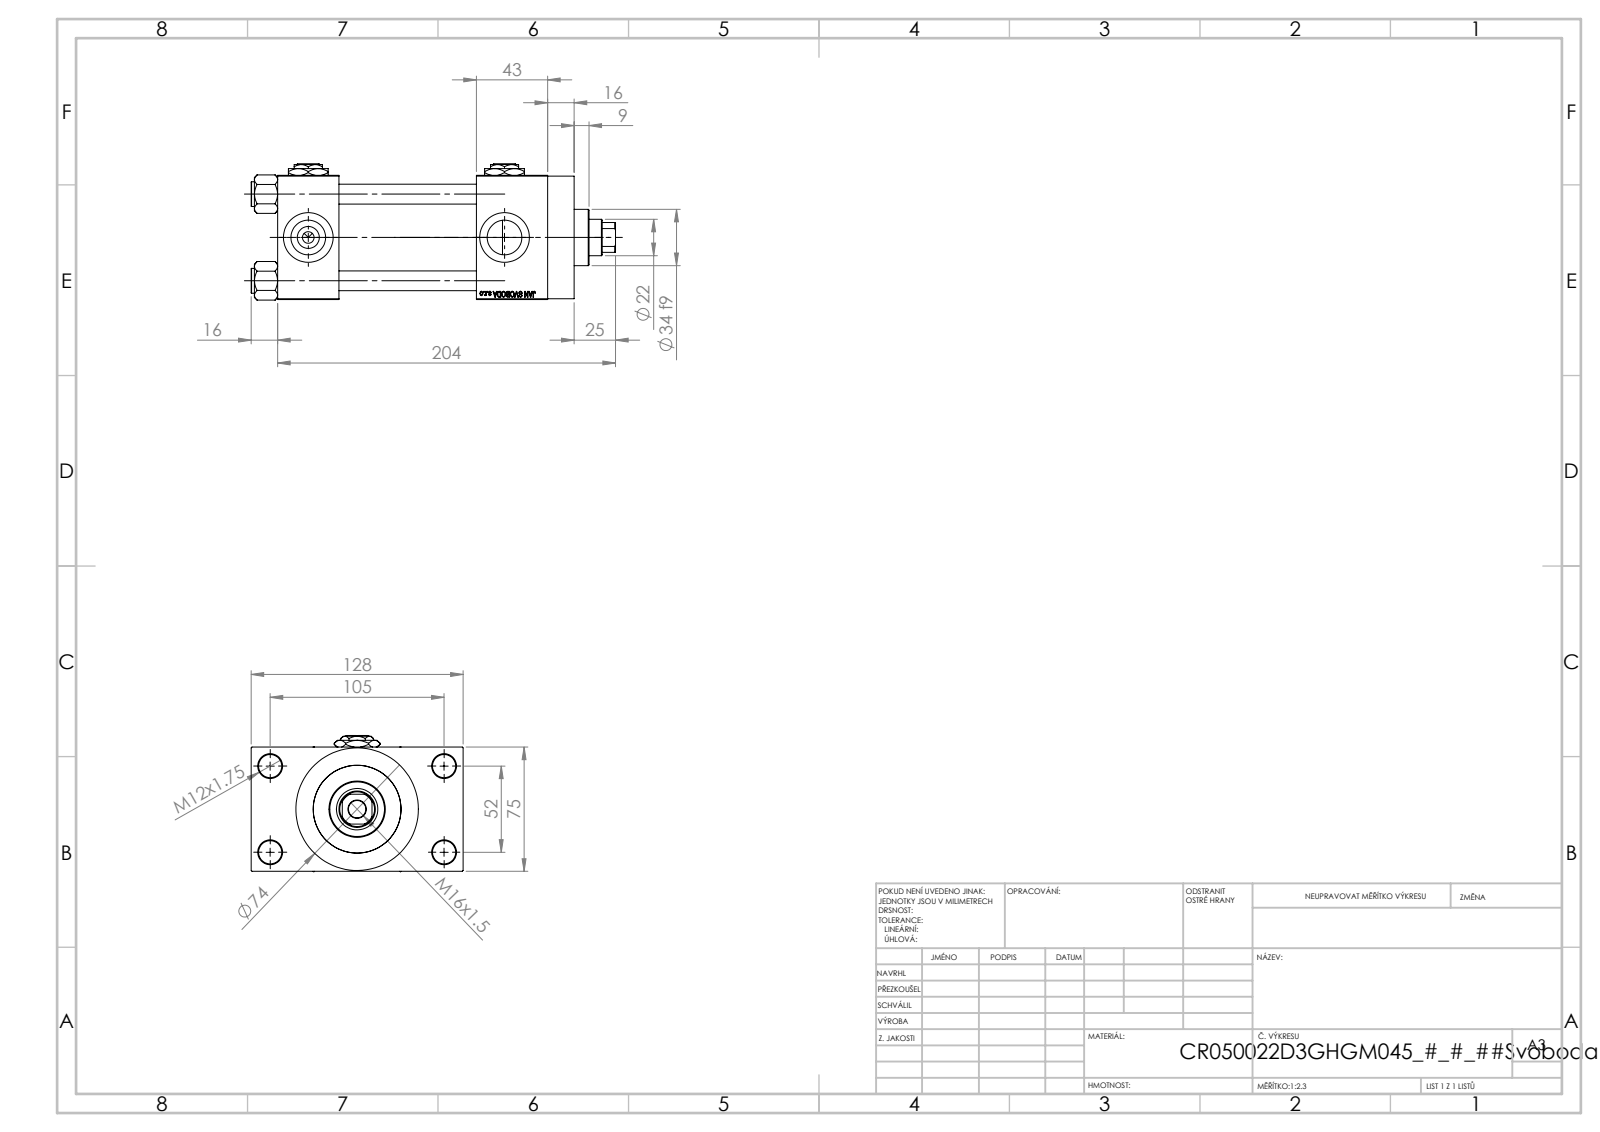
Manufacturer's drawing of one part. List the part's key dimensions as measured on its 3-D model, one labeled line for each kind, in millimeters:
Part name (STEP PRODUCT): V215CR_VCP_D; V215CR_D_Body; Zatka_pro_OIL_PORT; NUT_M5_D (+2 more)
STEP written by: SolidWorks 2019 (CONFIG_CONTROL_DESIGN)
Units: millimetres
Bodies: 13 solids, 1204 faces (545 planar, 99 cylindrical, 560 other)
Overall size (bounding box): 220 × 128 × 82.27
Volume: 826 433 mm³ · Surface area: 184 744 mm²
Round holes (diameter × count): ⌀12 ×4, ⌀14 ×4, ⌀20.96 ×4, ⌀30 ×4, ⌀7 ×3, ⌀10.5 ×1, ⌀22 ×1, ⌀25 ×1, ⌀41 ×1, ⌀50 ×1, ⌀53 ×1
Round bosses / shafts (diameter × count): ⌀15 ×4, ⌀74 ×1, ⌀56 ×1, ⌀34 ×1
Partial cylindrical surfaces — rounded edges, fillets, slot ends (radius × count): R10.5 ×1
Main face-to-face distances: 75, 83, 37, 120, 26.5, 126, 163, 43, 101.5, 16
Hole centre spacings: 26.35, 36.98, 52.3, 58.43, 58.59, 78.65, 94.37, 52
